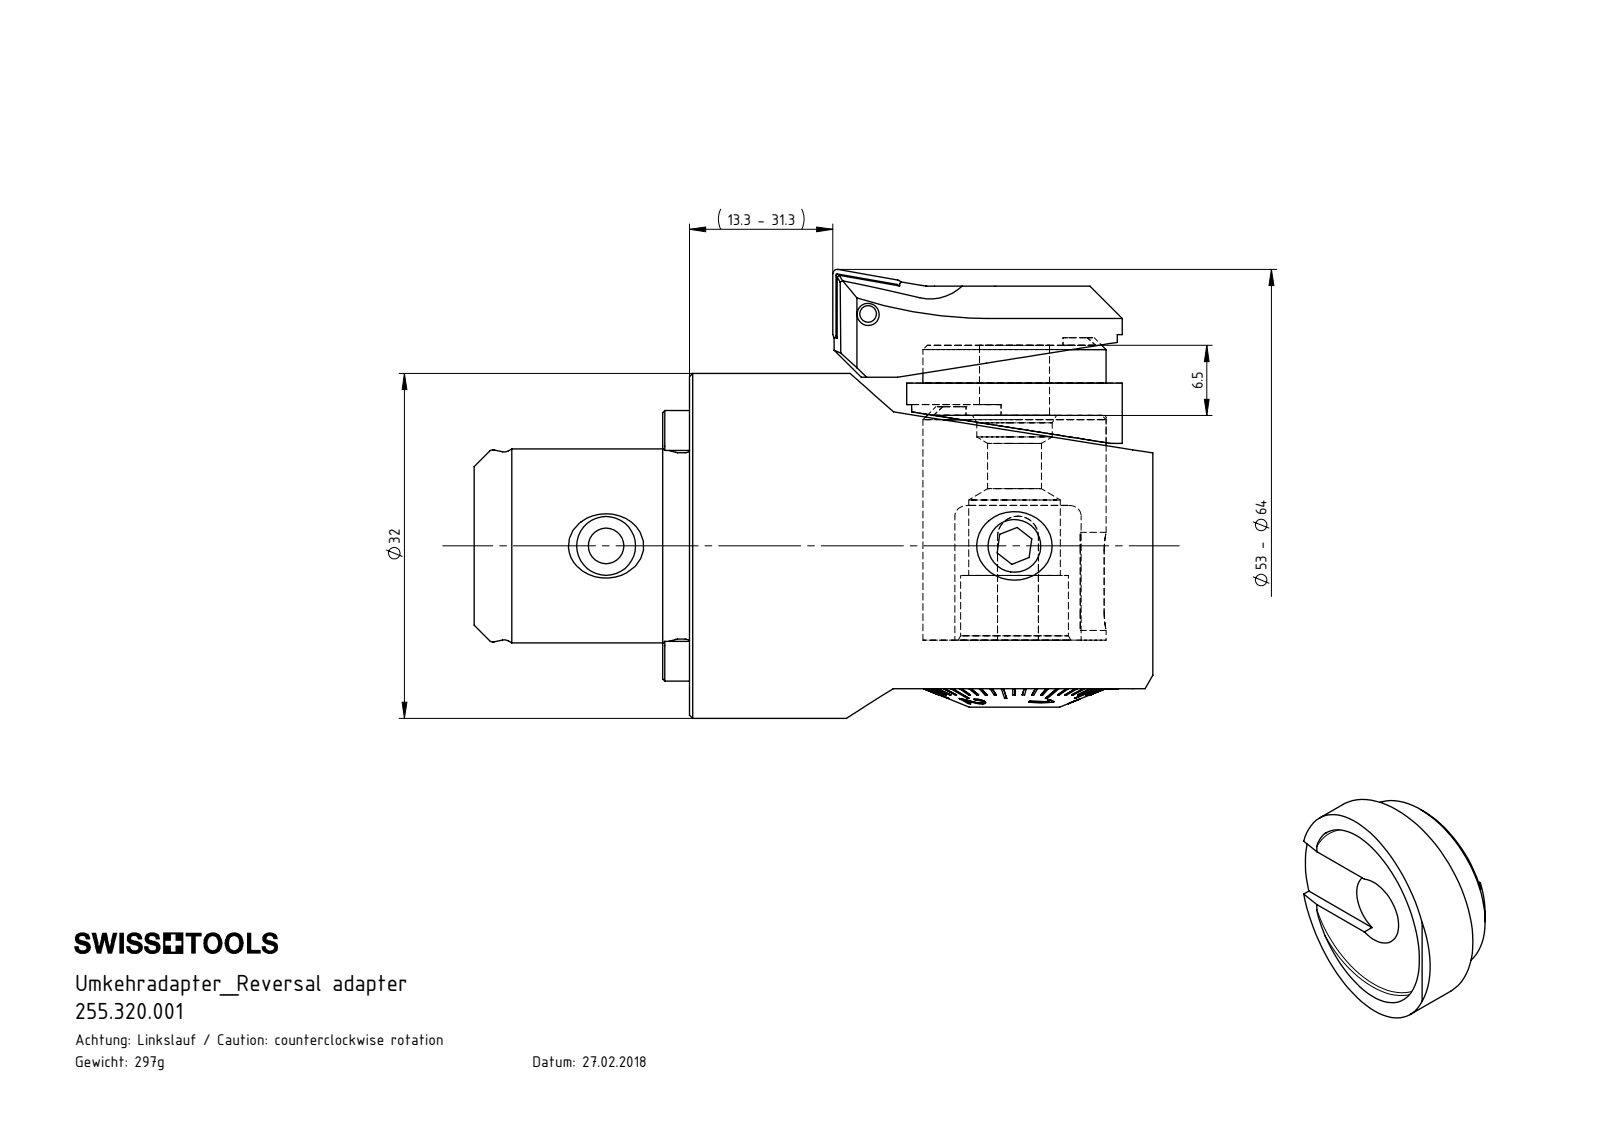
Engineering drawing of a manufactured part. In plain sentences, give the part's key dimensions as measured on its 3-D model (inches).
The part is named "F32-U00.001.006_B; 255.320.001". Its 3-D file was written by "SolidWorks 2017 (CONFIG_CONTROL_DESIGN)". It is 1 solid with 28 faces: 12 planar, 11 cylindrical and 5 other. Overall it measures 0.787 by 0.787 by 0.386 inches. Its volume is 0.097 cubic inches and its surface area 1.869 square inches. Round holes: 1 of diameter 0.256, 1 of diameter 0.669. Round bosses or shafts: 1 of diameter 0.787. Partial cylindrical surfaces (rounded edges, fillets, slot ends): 2 of radius 0.02. The main face-to-face distances are 0.256, 0.138, 0.118, 0.217, 0.079, 0.039, 0.028, 0.165, 0.244, 0.283.
